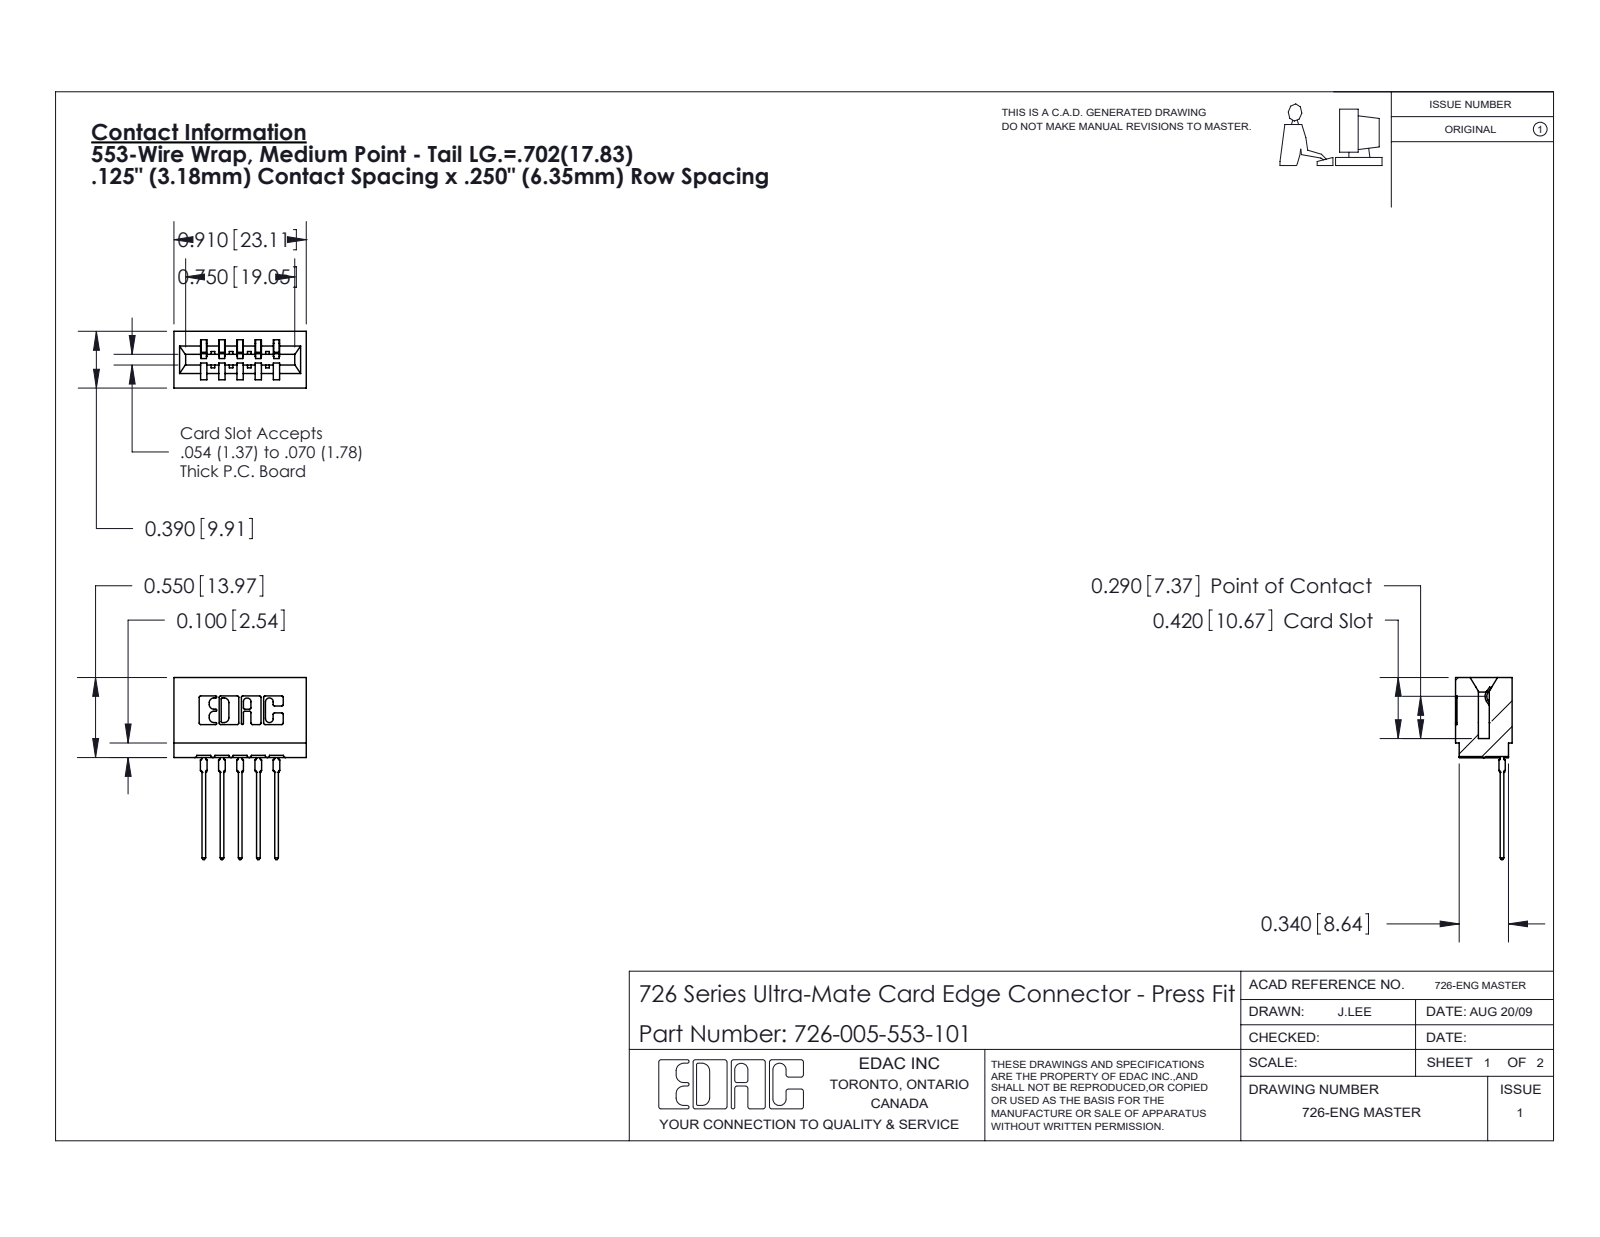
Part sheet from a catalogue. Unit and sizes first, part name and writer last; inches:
Units: inches
Overall size (bounding box): 1.251 × 0.91 × 0.39
Partial cylindrical surfaces — rounded edges, fillets, slot ends (radius × count): R0.01 ×22, R0.021 ×10, R0.007 ×6, R0.015 ×6, R0.031 ×6, R0.005 ×4, R0.011 ×4, R0.026 ×3
Main face-to-face distances: 0.25, 0.042, 0.057, 0.333, 0.125, 0.125, 0.083, 0.39, 0.025, 0.307
Volume: 0.14 in³ · Surface area: 4.727 in²
Bodies: 6 solids, 637 faces (370 planar, 137 cylindrical, 130 other)
Part name (STEP PRODUCT): 726 Part_.515 Slot Depth - 01; 746-292-001_553; 726-005-553-101
STEP written by: SolidWorks 2020 (CONFIG_CONTROL_DESIGN)
